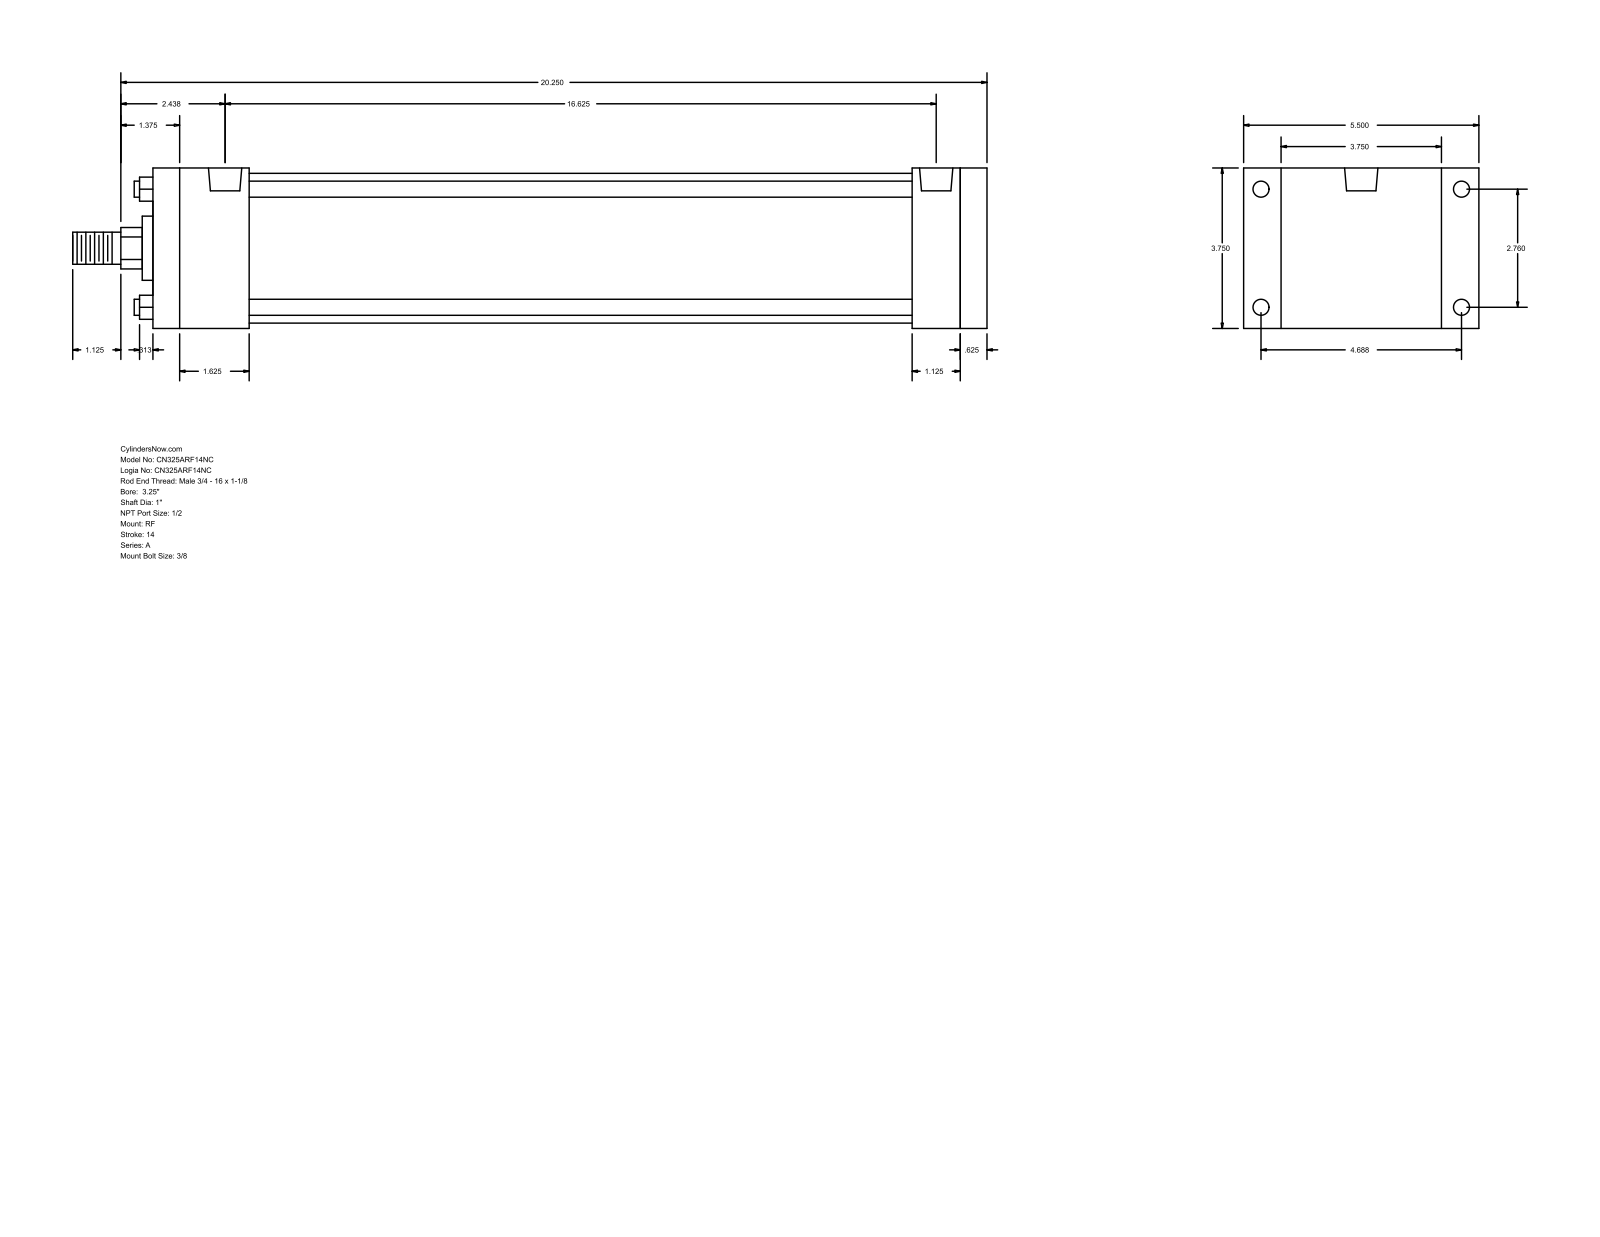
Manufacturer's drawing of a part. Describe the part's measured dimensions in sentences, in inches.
The part is named "A_RF__0325_1". Its 3-D file was written by "GSSL Pune (CONFIG_CONTROL_DESIGN)". It is 0 solids with 92 faces: 64 planar, 28 cylindrical and 0 other. Overall it measures 21.375 by 5.5 by 3.75 inches. Round holes: 4 of diameter 0.344, 4 of diameter 0.375, 2 of diameter 0.778. Round bosses or shafts: 4 of diameter 0.375, 1 of diameter 3.5, 1 of diameter 1.5, 1 of diameter 1, 1 of diameter 0.75. Partial cylindrical surfaces (rounded edges, fillets, slot ends): 1 of radius 0.484. The main face-to-face distances are 3.75, 19.5, 18.875, 0.625, 0.875, 4.625, 17.75, 1.125, 1.75, 2.25. The hole center spacings are 0.125, 2.76, 4.687, 5.439, 16.375, 16.5, 16.625.
